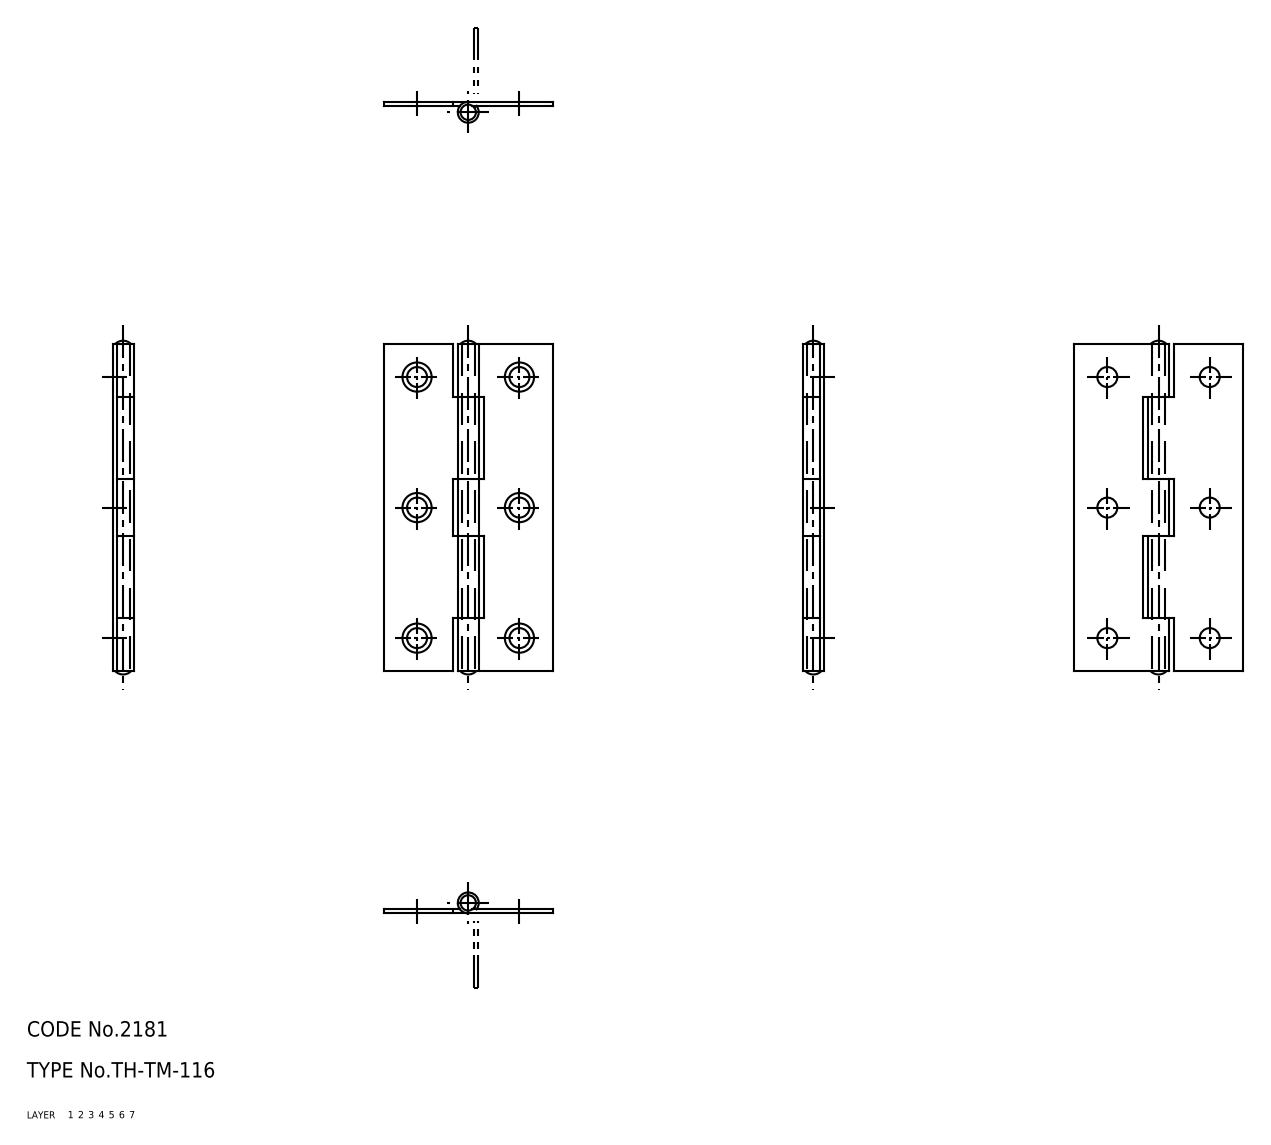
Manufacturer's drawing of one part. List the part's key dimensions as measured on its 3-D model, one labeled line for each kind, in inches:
Part name (STEP PRODUCT): 67112121; 67112134; 67112147
STEP written by: CADfix (AUTOMOTIVE_DESIGN)
Units: inches
Bodies: 3 solids, 56 faces (0 planar, 0 cylindrical, 56 other)
Overall size (bounding box): 2.567 × 1.299 × 0.161
Volume: 0.135 in³ · Surface area: 8.863 in²
